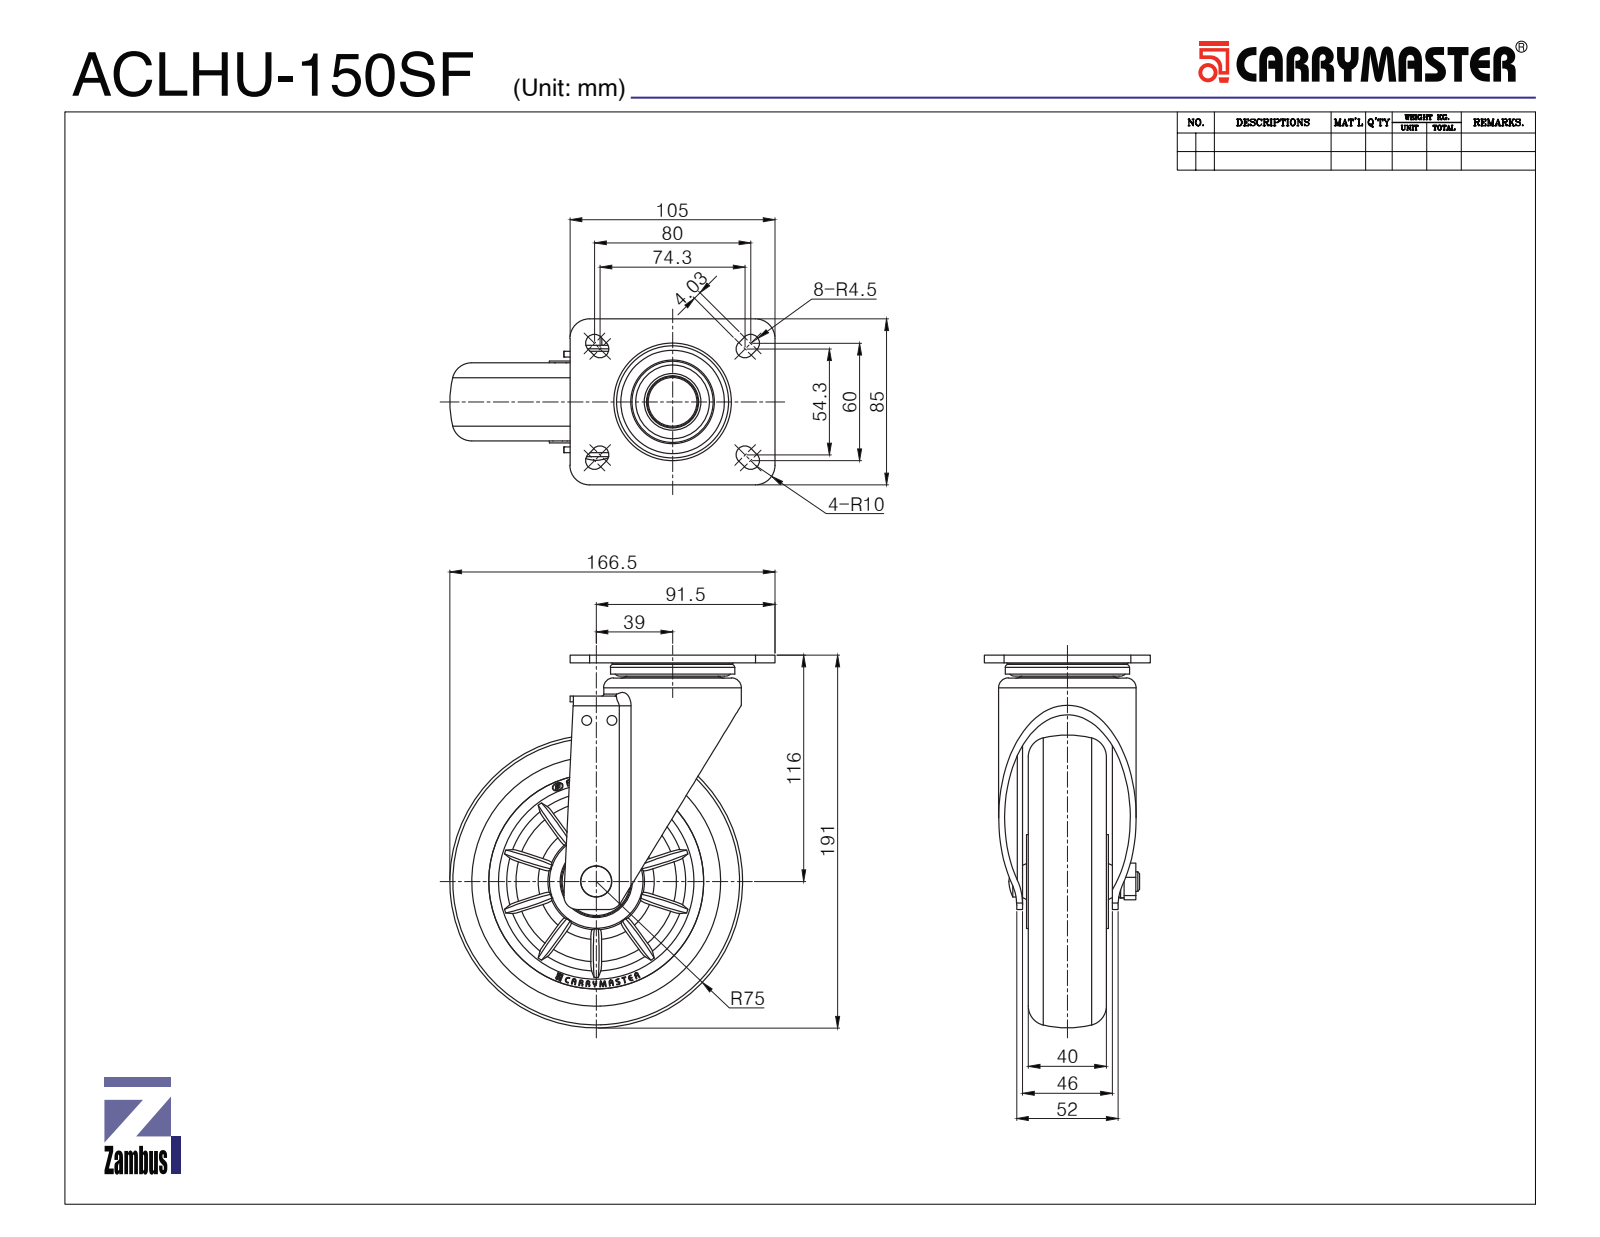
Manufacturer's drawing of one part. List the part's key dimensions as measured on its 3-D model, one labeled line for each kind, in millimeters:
Part name (STEP PRODUCT): ACLMU-150SF
STEP written by: SolidWorks 2015 (CONFIG_CONTROL_DESIGN)
Units: millimetres
Bodies: 13 solids, 1583 faces (875 planar, 236 cylindrical, 472 other)
Overall size (bounding box): 190.99 × 166.63 × 85
Volume: 691 546 mm³ · Surface area: 207 396 mm²
Round holes (diameter × count): ⌀1.7 ×2, ⌀5 ×2, ⌀8.5 ×1, ⌀10 ×1, ⌀12 ×1, ⌀14.6 ×1, ⌀30 ×1, ⌀32 ×1, ⌀32.08 ×1, ⌀44.9 ×1, ⌀51 ×1, ⌀60.3 ×1
Round bosses / shafts (diameter × count): ⌀0.65 ×2, ⌀130 ×1, ⌀70.42 ×1, ⌀63.7 ×1, ⌀60.5 ×1, ⌀57.3 ×1, ⌀35 ×1, ⌀19.36 ×1
Partial cylindrical surfaces — rounded edges, fillets, slot ends (radius × count): R1 ×44, R22 ×20, R4.5 ×8, R1.5 ×4, R10 ×4, R0.64 ×2, R0.83 ×2, R1.17 ×2
Main face-to-face distances: 3, 6, 4, 46, 23, 43, 40, 5, 18, 49
Hole centre spacings: 53.3, 13, 39.79, 82.62, 82.88, 132.45, 132.79, 134.23
